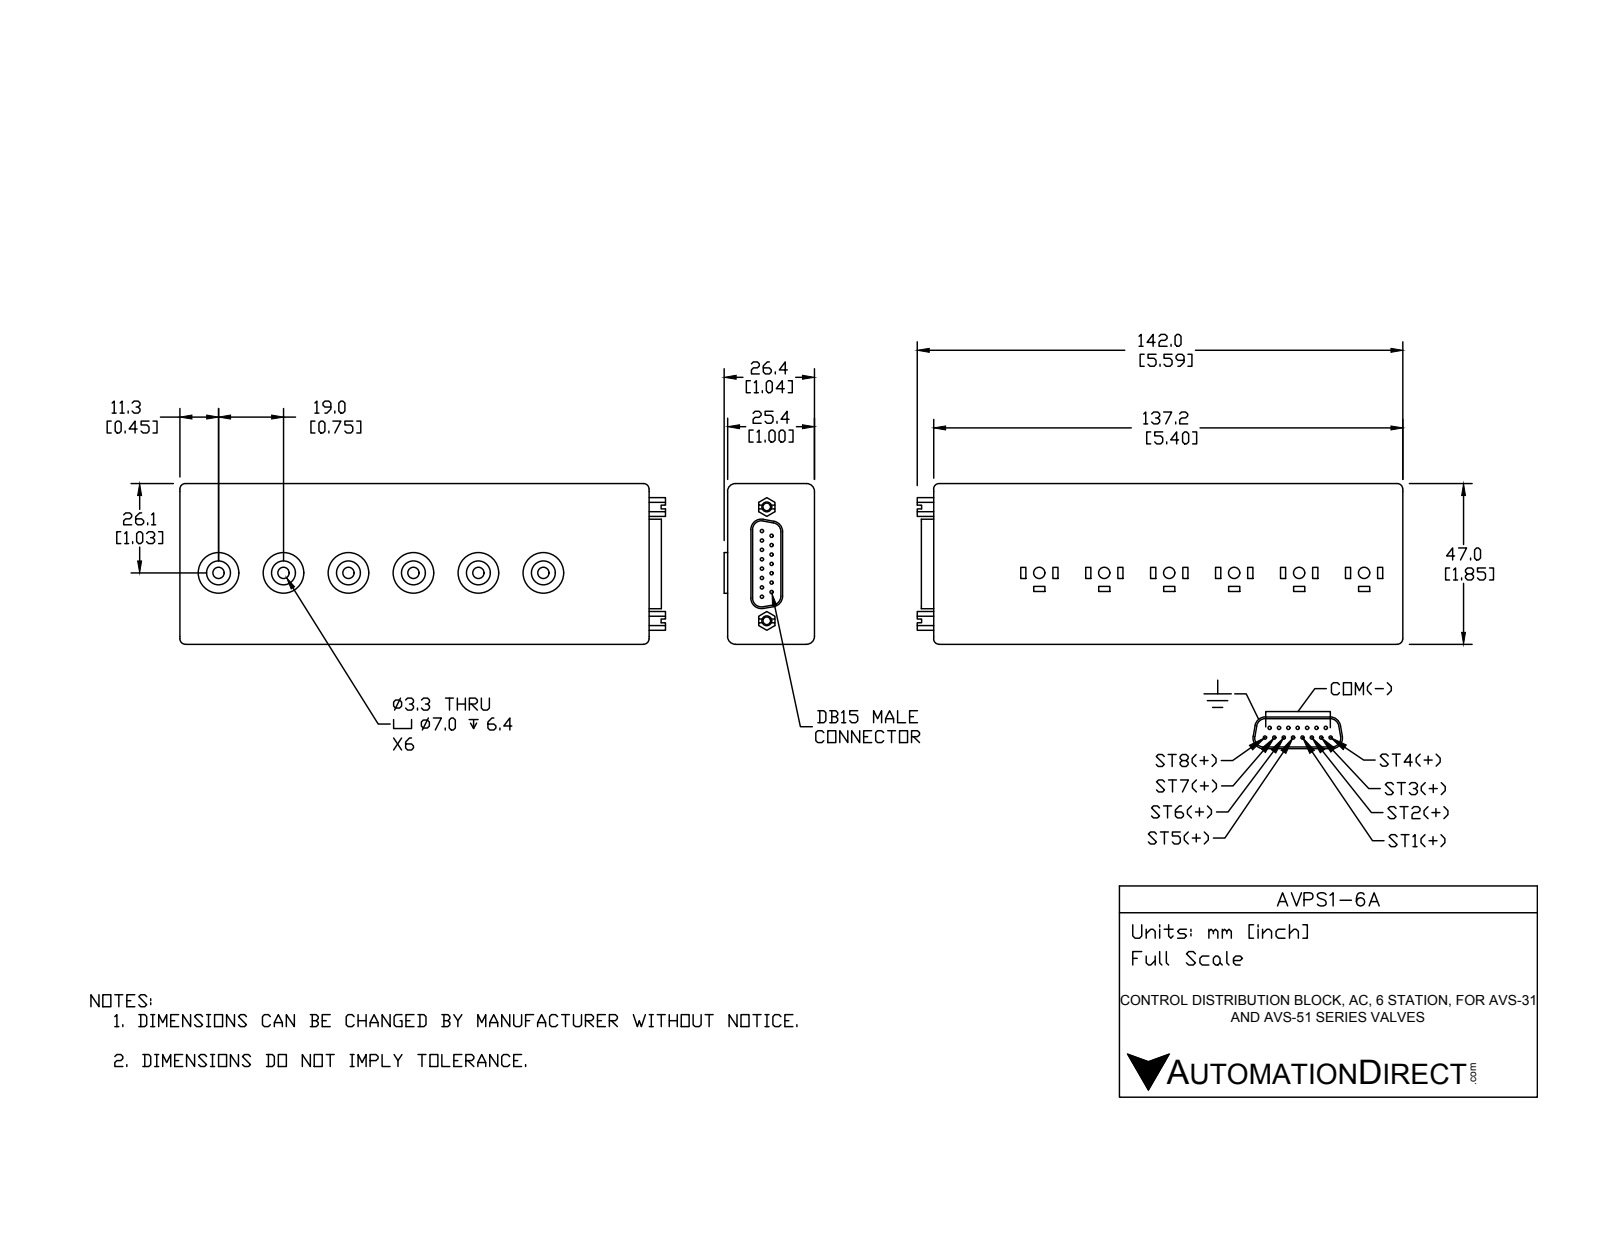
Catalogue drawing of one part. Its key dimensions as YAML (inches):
part_name: "AVPS1-6A"
step_written_by: "SolidWorks 2016 (AUTOMOTIVE_DESIGN)"
units: inches
bodies: {solids: 1, faces: 265, planar: 161, cylindrical: 92, other: 12}
overall_size: [5.592, 1.85, 1.04]
volume: 9.787
surface_area: 40.21
round_holes:
  - {diameter: 0.13, count: 6}
  - {diameter: 0.275, count: 6}
  - {diameter: 0.089, count: 2}
round_bosses_or_shafts:
  - {diameter: 0.039, count: 15}
  - {diameter: 0.469, count: 6}
partial_cylinders:
  - {radius: 0.062, count: 8}
  - {radius: 0.09, count: 4}
  - {radius: 0.102, count: 4}
  - {radius: 0.122, count: 4}
face_to_face_distances: [1, 1.85, 5.403, 0.04, 1.04, 0.25, 0.79, 0.059, 0.748, 0.123]
hole_center_spacings: [0.748, 1.496, 2.244, 2.992, 1.311, 3.74]
